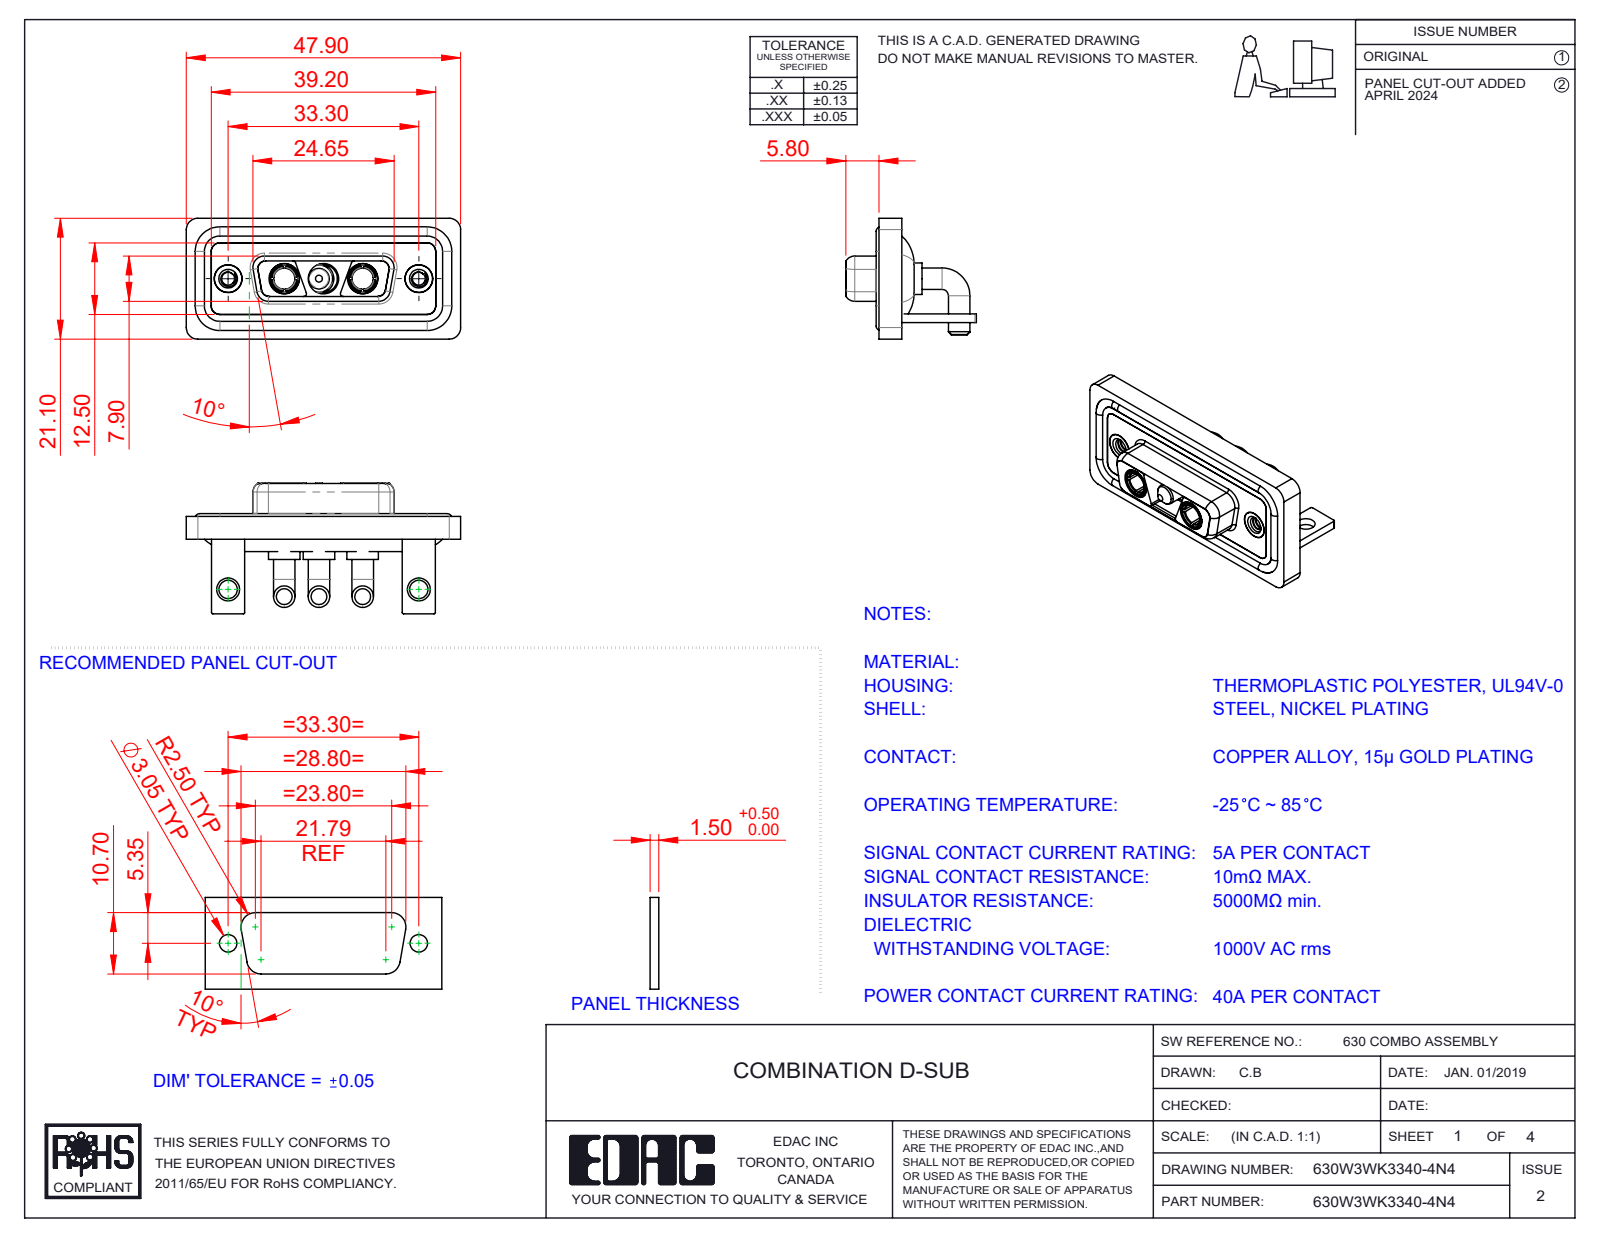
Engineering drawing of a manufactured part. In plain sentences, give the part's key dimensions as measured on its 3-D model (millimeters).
The part is named "630Combo Threaded Rivet_2; Power Pin_40A RA; 630Combo Housing_3WK3; 630Combo Stabilizer Bracket_50 Contacts (+5 more)". Its 3-D file was written by "SolidWorks 2023 (CONFIG_CONTROL_DESIGN)". It is 15 solids with 643 faces: 198 planar, 288 cylindrical and 157 other. Overall it measures 47.9 by 22.8 by 21.1 millimeters. Its volume is 6 617 cubic millimeters and its surface area 10 605 square millimeters. Round holes: 5 of diameter 4.85, 3 of diameter 5.3, 2 of diameter 2.26, 2 of diameter 3.2, 2 of diameter 3.7, 2 of diameter 4, 2 of diameter 4.05, 2 of diameter 5. Round bosses or shafts: 6 of diameter 3.75, 4 of diameter 1.6, 3 of diameter 5.5, 3 of diameter 5.2, 3 of diameter 4.75, 2 of diameter 4.96, 2 of diameter 4.95, 2 of diameter 4.8. Partial cylindrical surfaces (rounded edges, fillets, slot ends): 21 of radius 2, 18 of radius 1.5, 16 of radius 0.25, 12 of radius 1.35, 9 of radius 0.5, 8 of radius 1.6, 4 of radius 0.6, 4 of radius 0.65. The main face-to-face distances are 0.4, 2.9, 1.5, 3.7, 1.8, 1.1, 4.1, 1.6, 2.5, 1.4. The hole center spacings are 6.85, 9.8, 16.65, 23.5, 33.3, 13.7.
